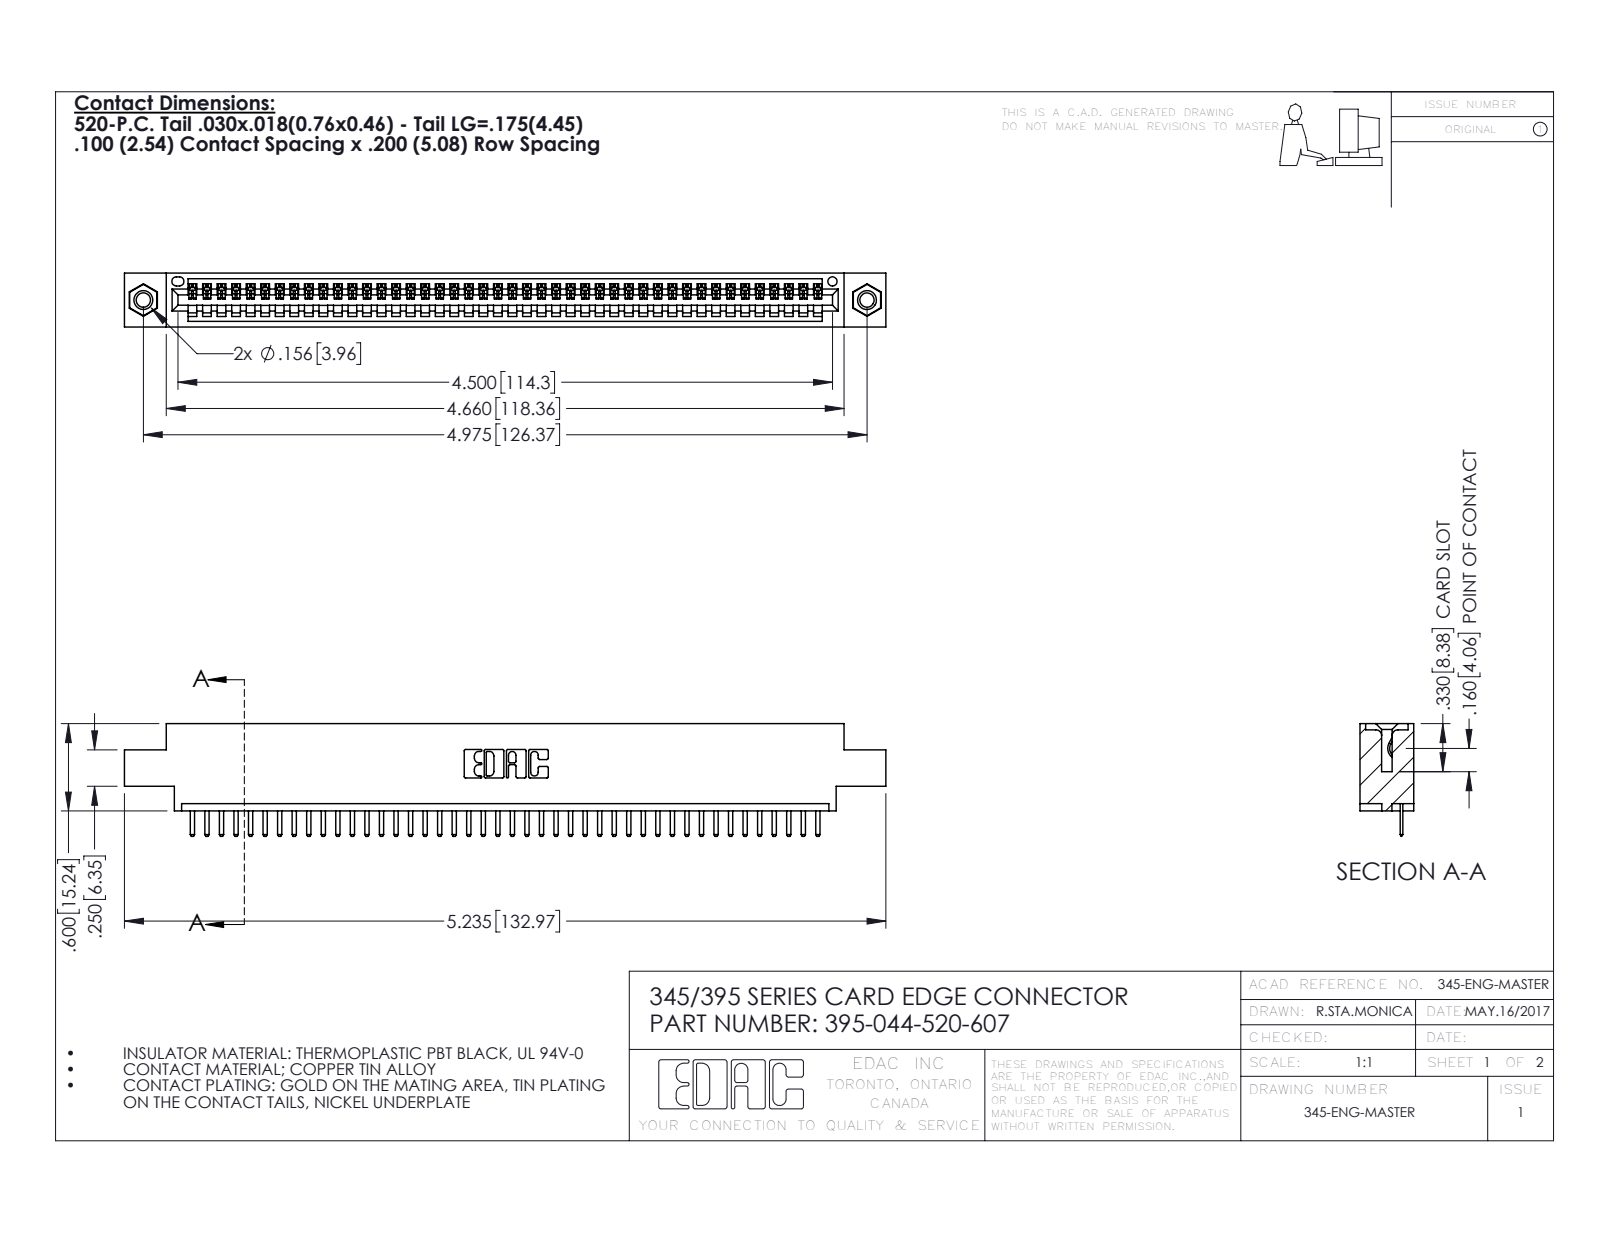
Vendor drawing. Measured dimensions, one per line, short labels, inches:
name: 345-292-001_345-293-120; 395-044-520-607; 345 Part_0.170 Offset - 0.156 Dia-TI; 345-250-001_345-250-005-103
written by: SolidWorks 2016 (CONFIG_CONTROL_DESIGN)
unit: in
bodies: 47 solids, 2918 faces (1964 planar, 938 cylindrical, 16 other)
size: 5.235 × 0.775 × 0.37
volume: 0.756 in³; area: 25.17 in²
holes: 2× ⌀0.098, 2× ⌀0.125, 2× ⌀0.156, 1× ⌀0.064
bosses: 2× ⌀0.155
rounds: 90× R0.01, 88× R0.006, 22× R0.01, 6× R0.007, 6× R0.031, 3× R0.026, 2× R0.031, 2× R0.04
face distances: 0.072, 0.298, 0.37, 0.2, 0.098, 0.272, 0.025, 0.225, 0.072, 0.175
hole spacings: 0.27, 4.739, 4.975
